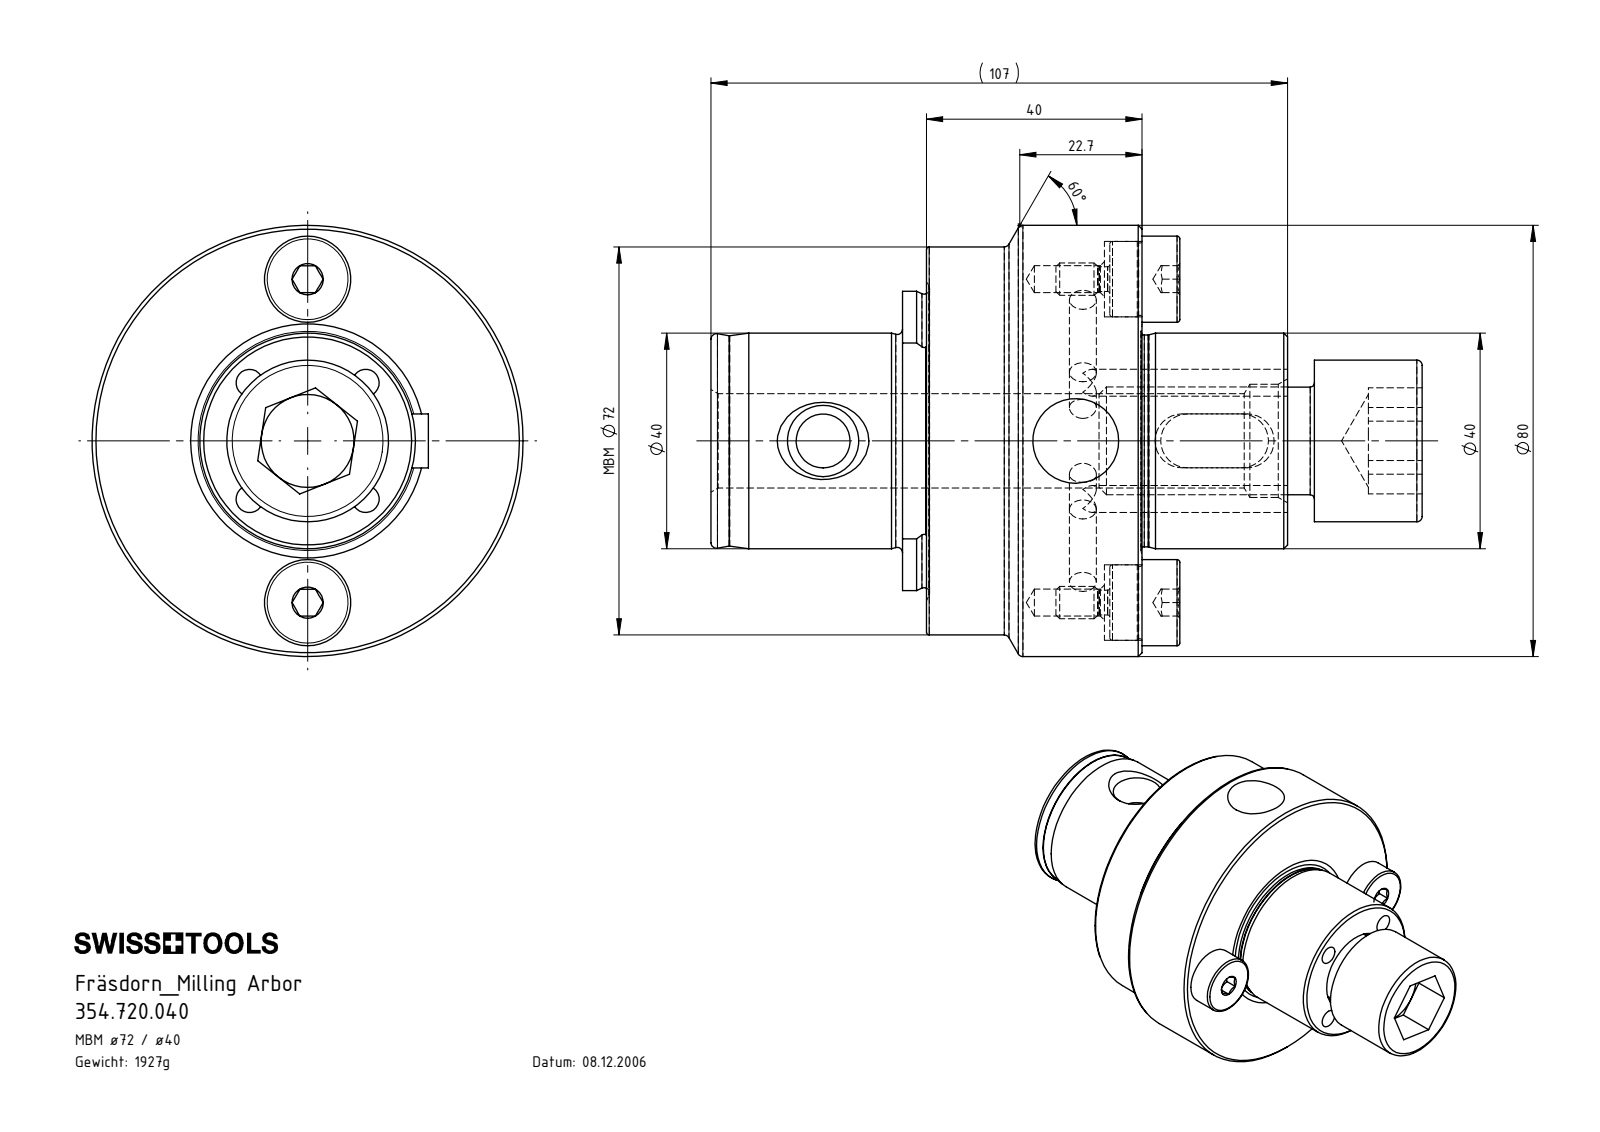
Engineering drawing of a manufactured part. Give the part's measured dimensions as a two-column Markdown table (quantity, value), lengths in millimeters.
| quantity | value |
| --- | --- |
| part name | 354.720.040; D40-ER3.001.022_A; D40-ER2.002.016_A; D40-ER1.K61.030 (+4 more) |
| STEP written by | SolidWorks 2017 (CONFIG_CONTROL_DESIGN) |
| units | millimeters |
| bodies | 8 solids, 355 faces (76 planar, 144 cylindrical, 135 other) |
| overall size | 125 × 80 × 80 |
| volume | 276 031 mm³ |
| surface area | 54 154 mm² |
| round holes (diameter × count) | 3 × 12, 5 × 4, 6.5 × 1, 10 × 1, 10.5 × 1, 17.5 × 1, 21 × 1, 29 × 1 |
| round bosses / shafts (diameter × count) | 80 × 1, 72 × 1, 52 × 1, 40 × 1, 39.3 × 1, 30 × 1, 20 × 1, 10 × 1 |
| partial cylindrical surfaces (radius × count) | 5 × 4, 8 × 1, 27.77 × 1 |
| main face-to-face distances | 40, 45, 34, 11, 74, 85, 65, 16, 80, 114 |
| hole center spacings | 18, 31.17, 3.44, 15, 15.25, 18.52, 27.74, 29.8 |
